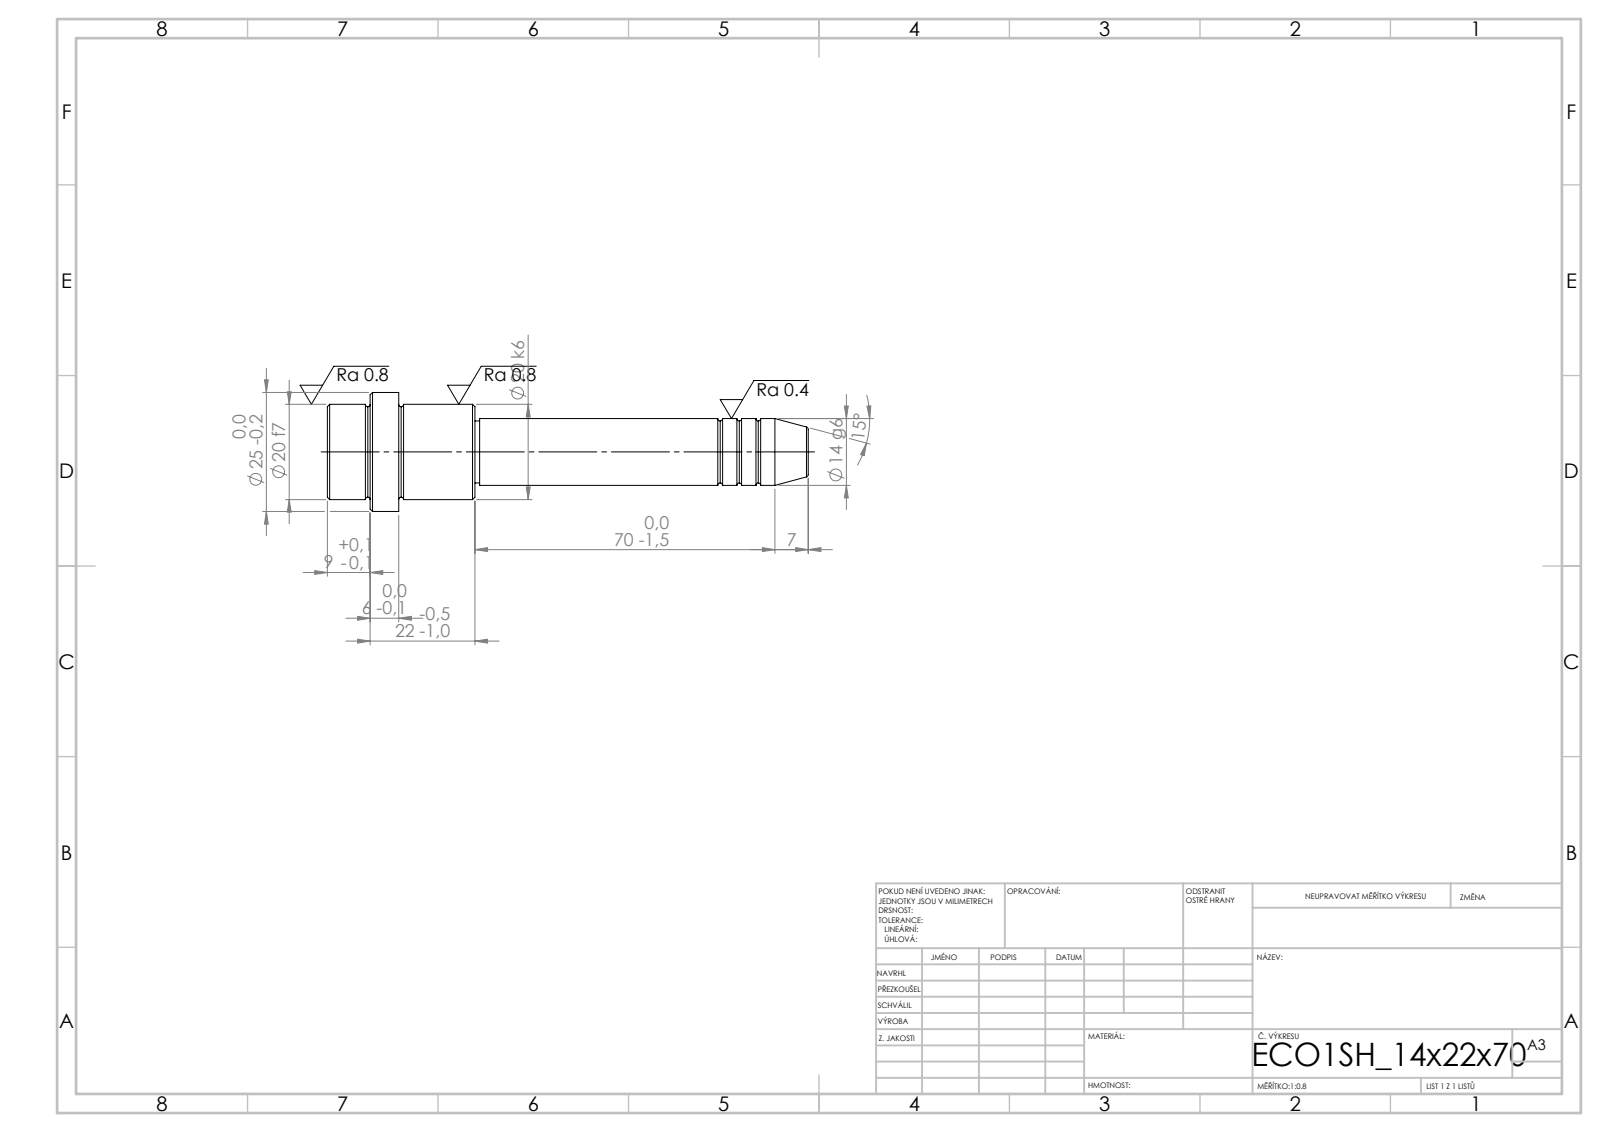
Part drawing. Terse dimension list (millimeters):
written by: SolidWorks 2019 (CONFIG_CONTROL_DESIGN)
unit: mm
bodies: 1 solid, 52 faces (6 planar, 16 cylindrical, 30 other)
size: 101 × 25 × 25
volume: 21 166 mm³; area: 6 105 mm²
bosses: 1× ⌀25, 1× ⌀20, 1× ⌀14, 1× ⌀13
face distances: 15, 16, 31, 22, 6, 9, 70, 86, 92, 101
